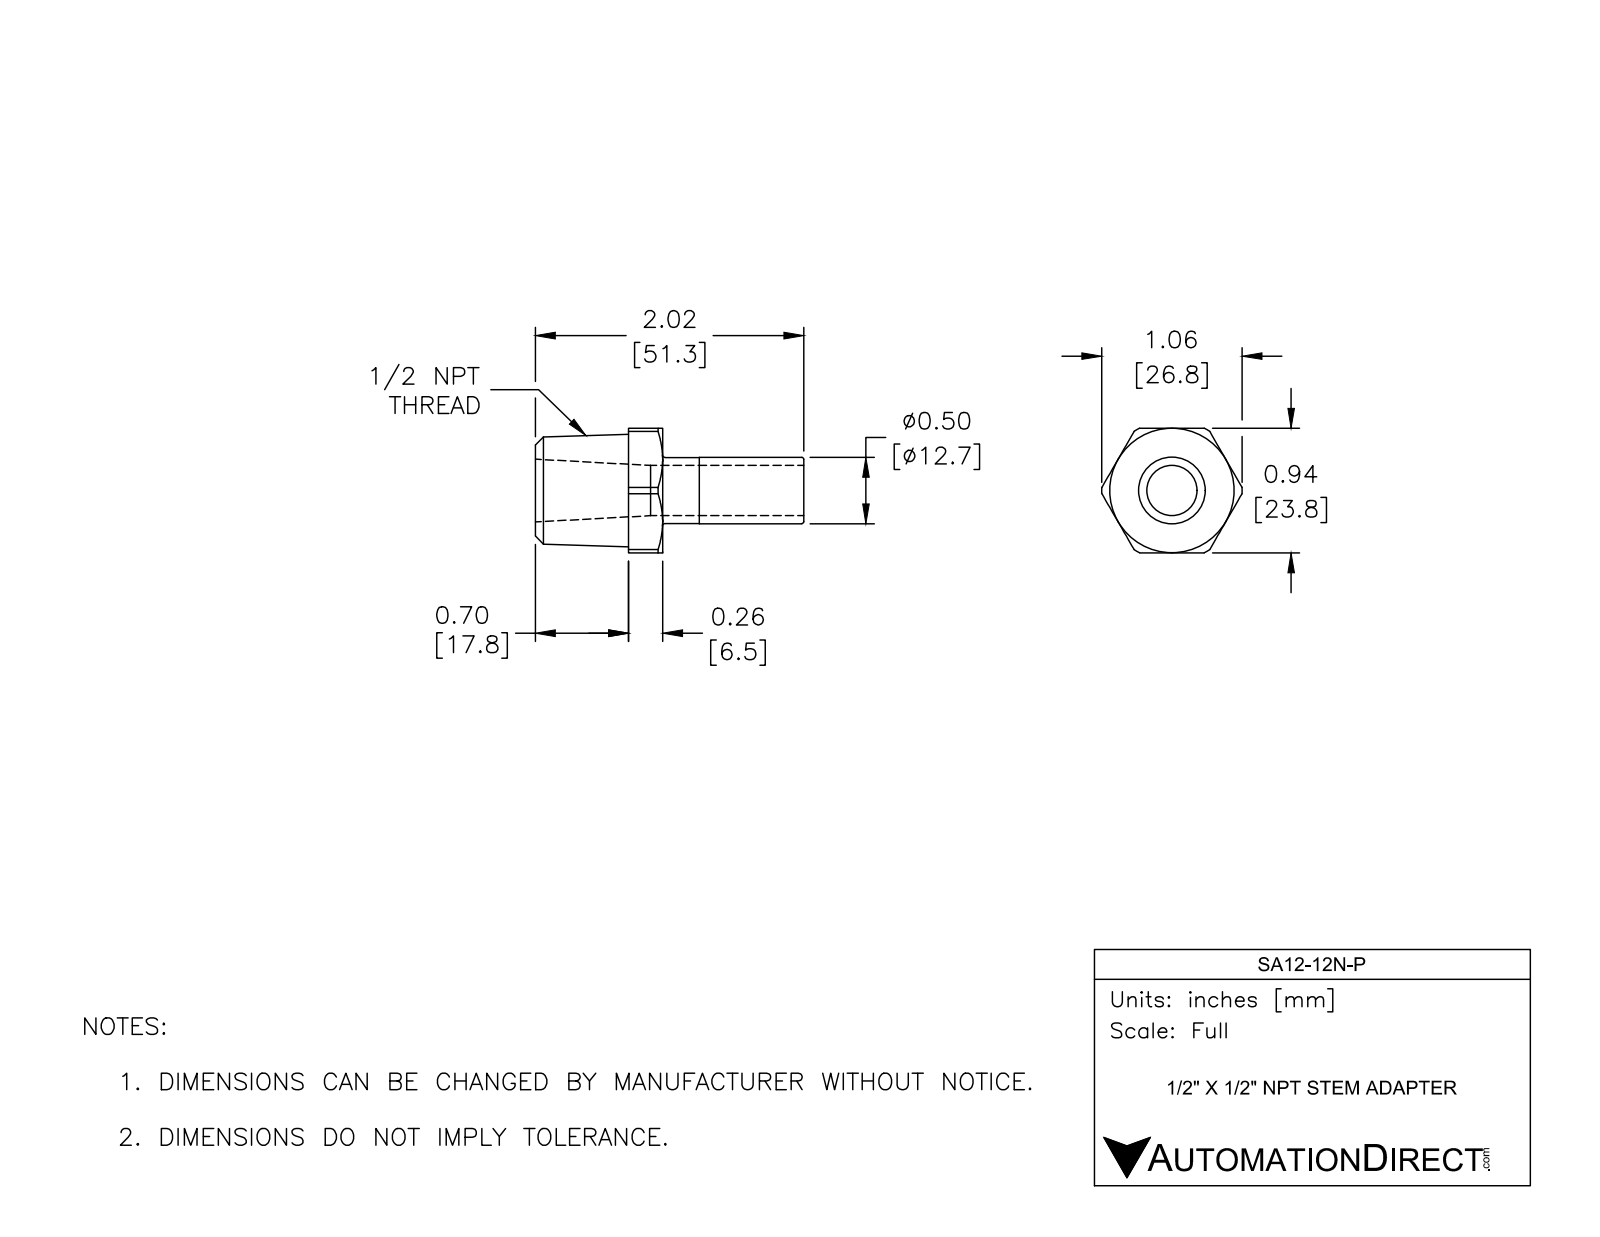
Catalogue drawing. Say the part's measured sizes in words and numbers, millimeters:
The part is named "SA12-12N-P". Its 3-D file was written by "SolidWorks 2017 (AUTOMOTIVE_DESIGN)". It is 1 solid with 41 faces: 11 planar, 13 cylindrical and 17 other. Overall it measures 51.3 by 26.8 by 23.8 millimeters. Its volume is 8 490 cubic millimeters and its surface area 5 073 square millimeters. Round holes: 1 of diameter 9.6. Round bosses or shafts: 1 of diameter 12.7, 1 of diameter 12.6. Partial cylindrical surfaces (rounded edges, fillets, slot ends): 1 of radius 13.4. The main face-to-face distances are 23.8, 6.5, 17.8, 24.3, 51.3, 33.5, 27, 31.3, 13.5, 7.
